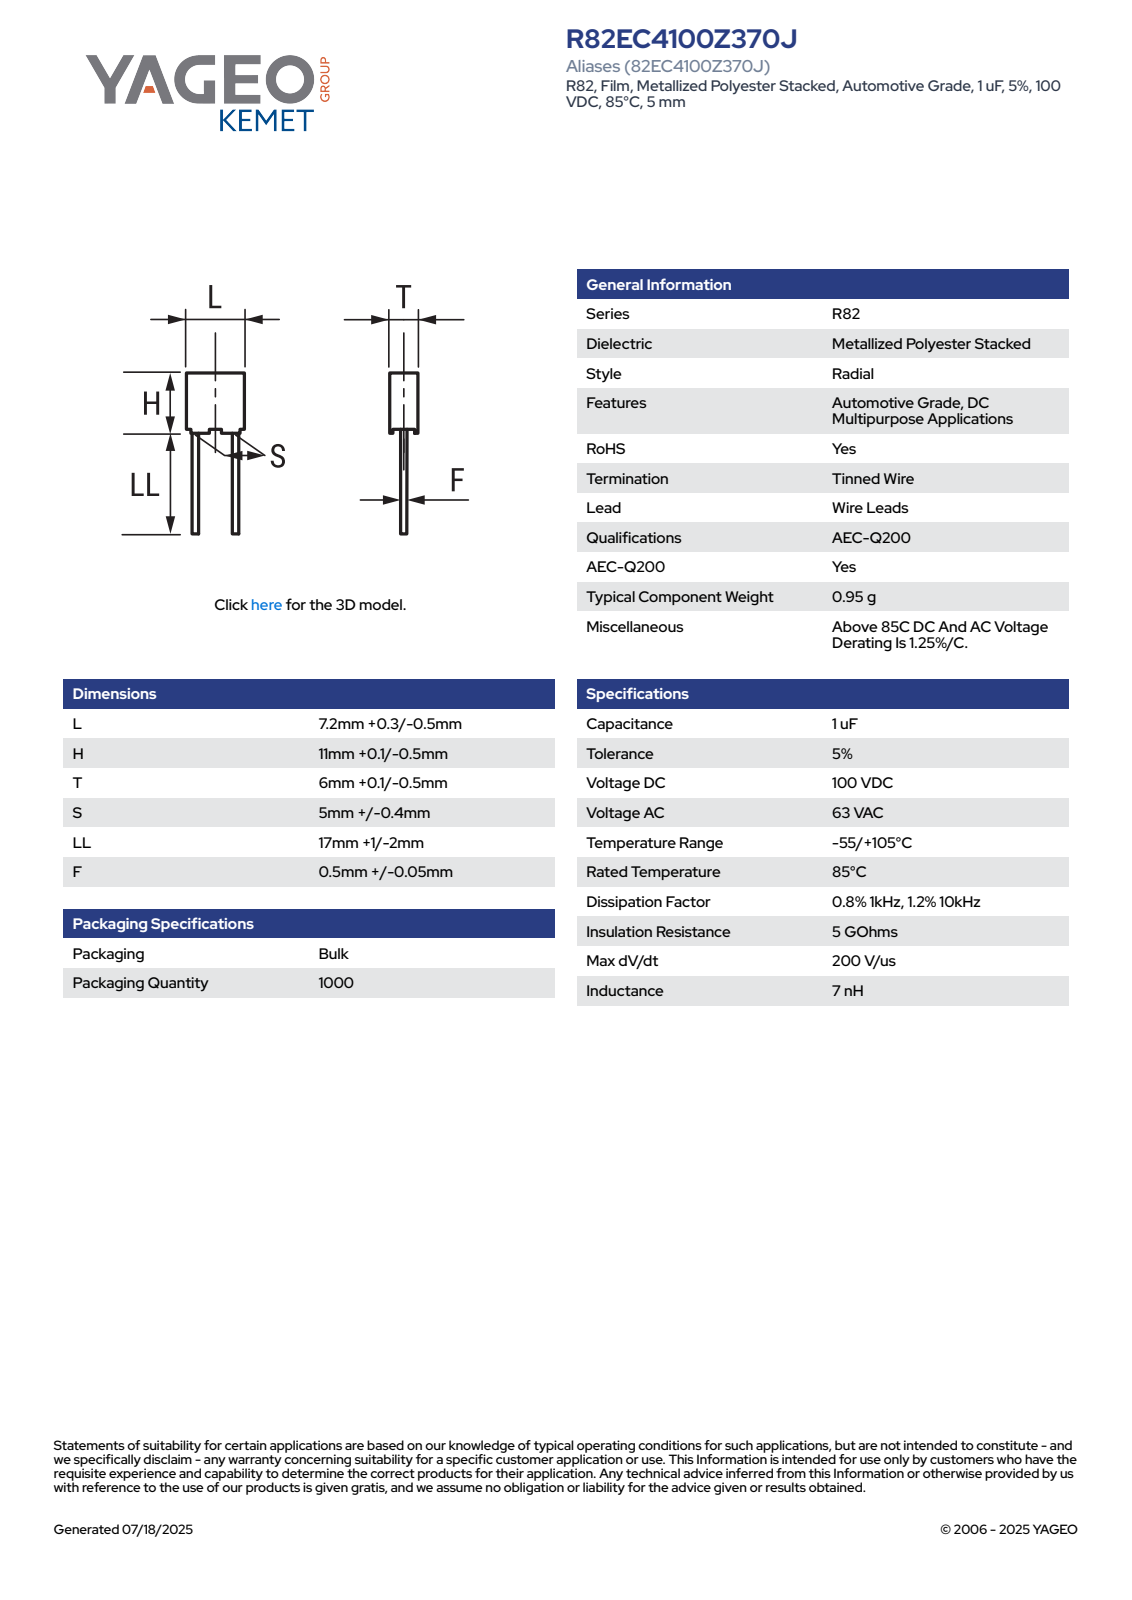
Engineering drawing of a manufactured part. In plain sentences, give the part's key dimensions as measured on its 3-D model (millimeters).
The part is named "CFR_RB3_7.2X11X6_L7.5H11.1T6.1S5LL18F0.55". Its 3-D file was written by "SolidWorks 2014 (AUTOMOTIVE_DESIGN)". It is 4 solids with 85 faces: 77 planar, 8 cylindrical and 0 other. Overall it measures 29.1 by 7.5 by 6.11 millimeters. Its volume is 486 cubic millimeters and its surface area 473 square millimeters. Round bosses or shafts: 2 of diameter 0.55. Partial cylindrical surfaces (rounded edges, fillets, slot ends): 4 of radius 0.5. The main face-to-face distances are 6.1, 7.5, 10.35, 5.85, 7.25, 0.75, 11.1, 5.6, 7, 0.38.
